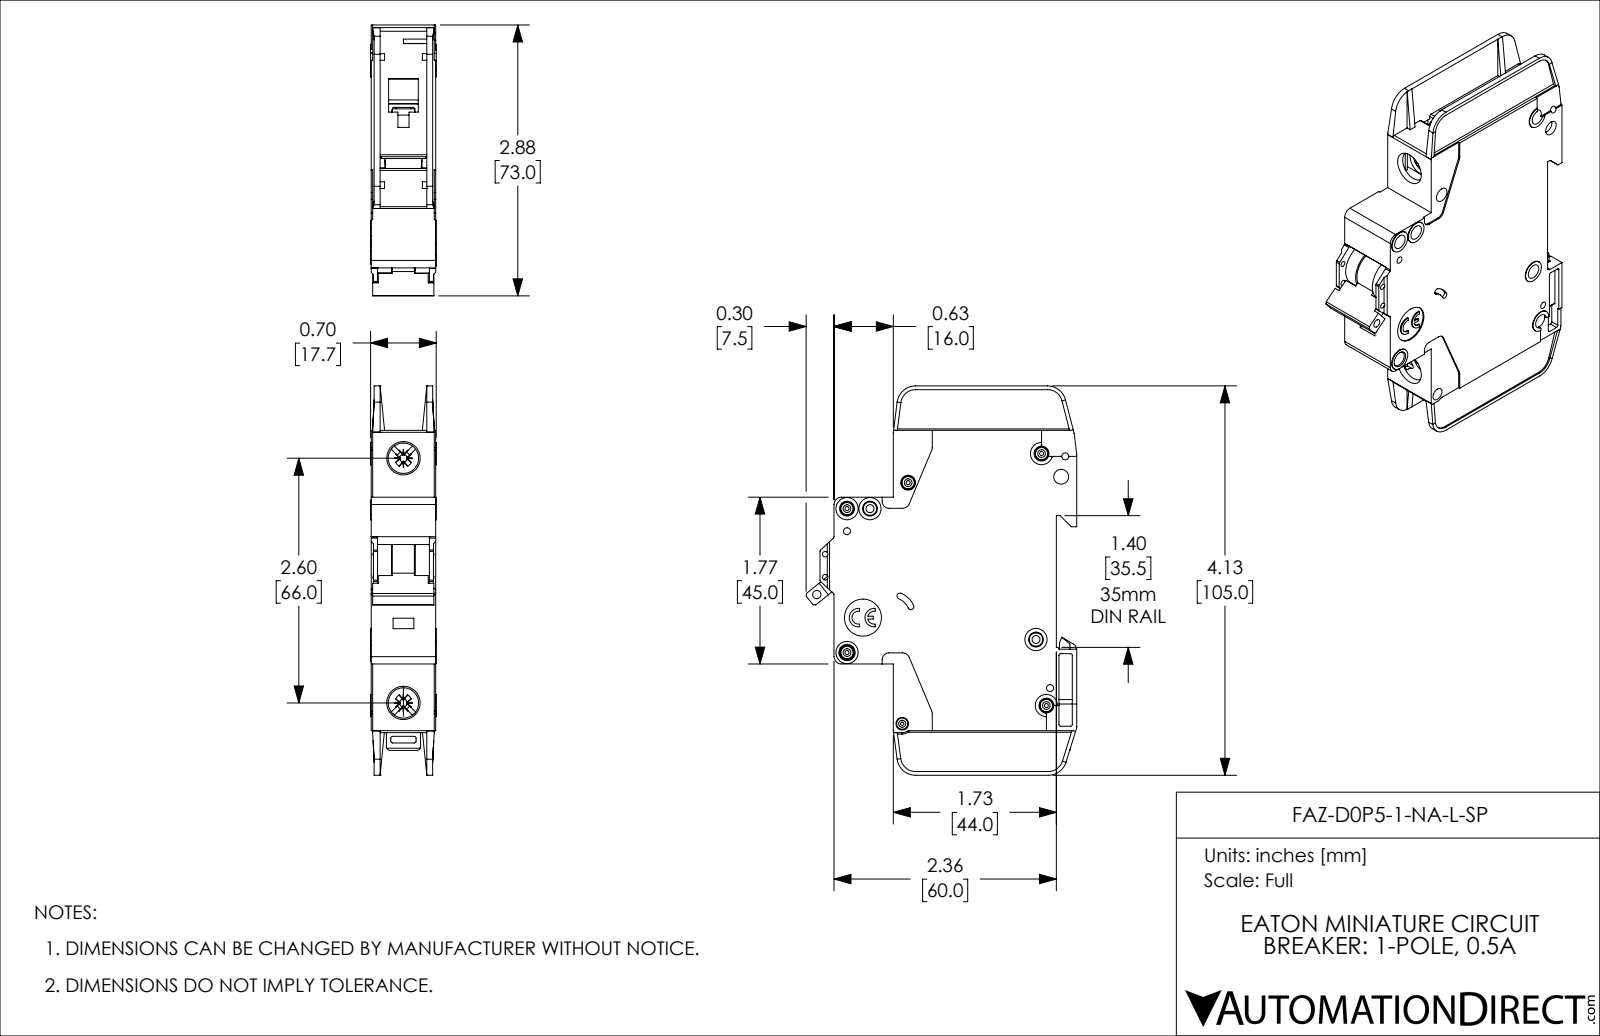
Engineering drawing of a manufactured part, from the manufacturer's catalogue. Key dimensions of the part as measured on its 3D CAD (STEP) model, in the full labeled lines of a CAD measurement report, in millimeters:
Part name (STEP PRODUCT): FAZ-D0P5-1-NA-L-SP
STEP written by: SolidWorks 2019 (AUTOMOTIVE_DESIGN)
Units: millimetres
Bodies: 1 solid, 1127 faces (671 planar, 357 cylindrical, 99 other)
Overall size (bounding box): 105 × 73.1 × 17.7
Volume: 76 720 mm³ · Surface area: 26 460 mm²
Round holes (diameter × count): ⌀4 ×8, ⌀1.1 ×5, ⌀1.9 ×4, ⌀1.5 ×2, ⌀2.2 ×2, ⌀8.2 ×2, ⌀0.9 ×1, ⌀2.3 ×1, ⌀2.5 ×1, ⌀3.4 ×1, ⌀10 ×1
Round bosses / shafts (diameter × count): ⌀3.3 ×5, ⌀6 ×4, ⌀3 ×2, ⌀2.5 ×1
Partial cylindrical surfaces — rounded edges, fillets, slot ends (radius × count): R0.5 ×42, R0.4 ×10, R1 ×10, R2 ×8, R5 ×5, R0.2 ×4, R0.7 ×4, R1.1 ×4
Main face-to-face distances: 1.2, 17.4, 15, 16.2, 2.4, 13.8, 0.4, 0.8, 12.6, 14.6
Hole centre spacings: 6.2, 13.6, 22.1, 4.8, 5.1, 5.2, 5.6, 6.1
